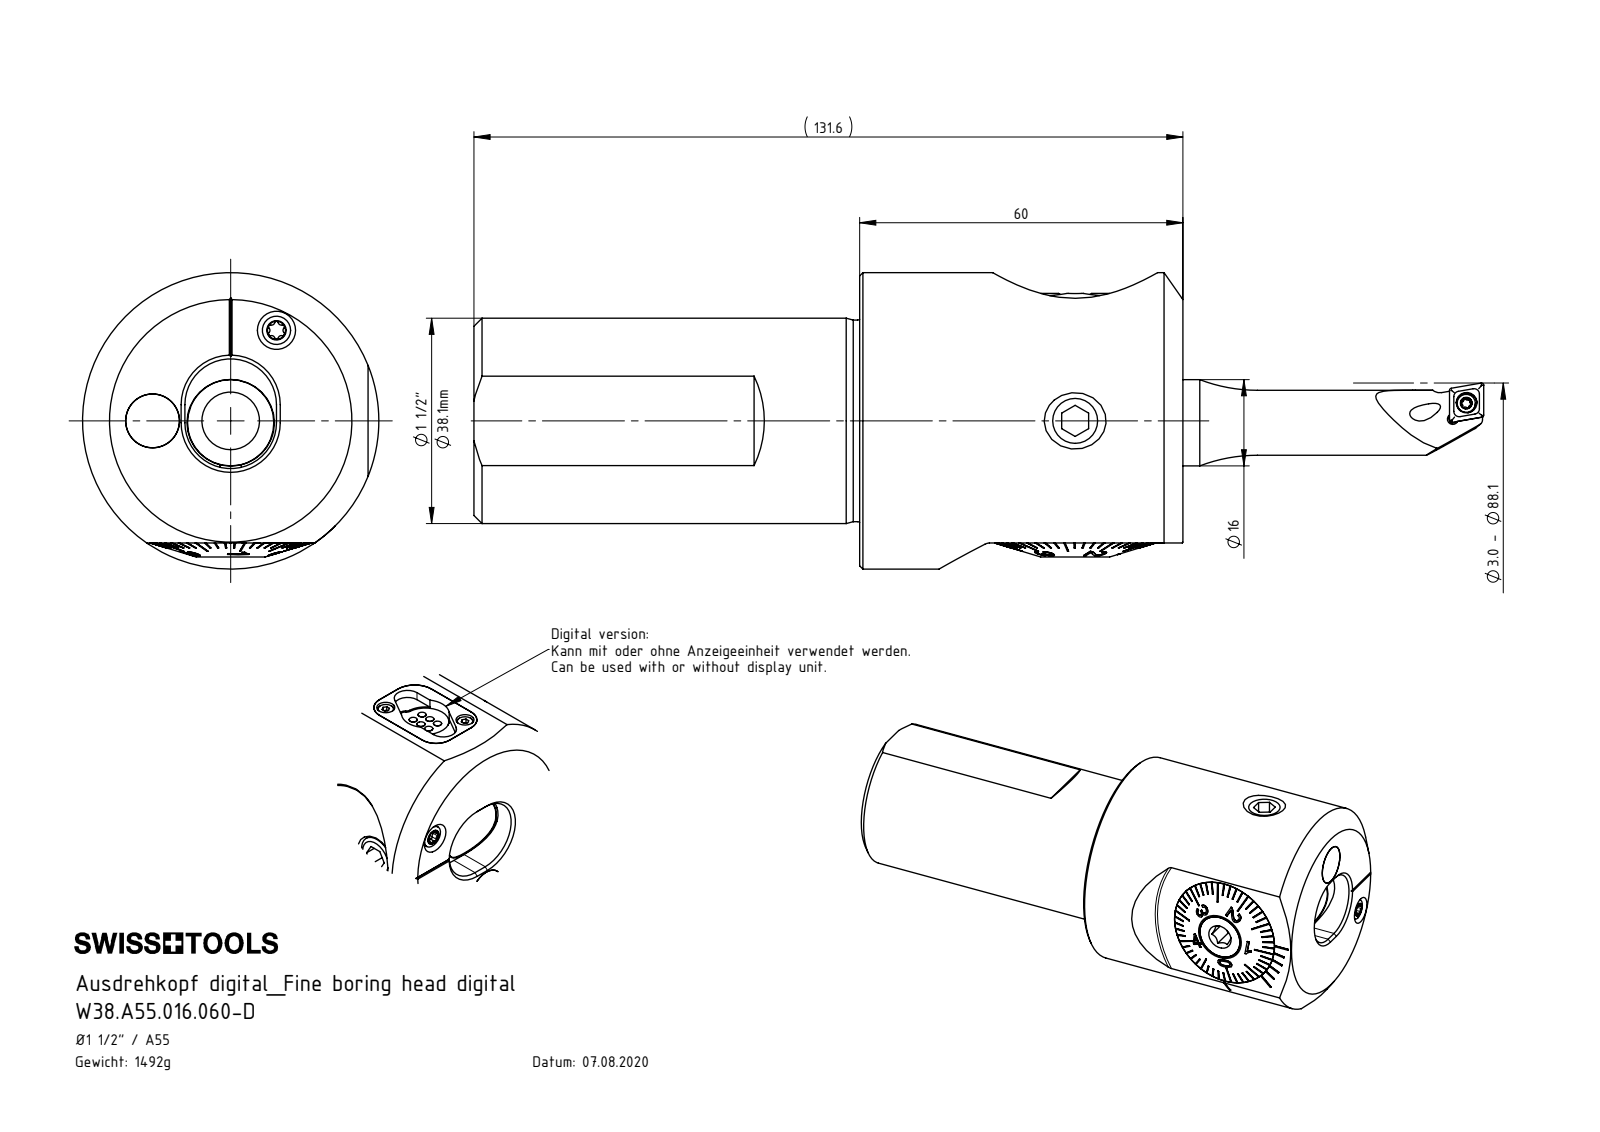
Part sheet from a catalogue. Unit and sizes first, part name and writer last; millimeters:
Units: millimetres
Overall size (bounding box): 131.6 × 55 × 55
Round holes (diameter × count): ⌀1.6 ×3, ⌀4.2 ×3, ⌀8.5 ×3, ⌀2.2 ×2, ⌀3.3 ×1, ⌀8 ×1, ⌀10 ×1, ⌀10.1 ×1, ⌀10.7 ×1, ⌀11.1 ×1, ⌀11.4 ×1, ⌀12.4 ×1
Round bosses / shafts (diameter × count): ⌀1.9 ×6, ⌀10 ×3, ⌀3.8 ×2, ⌀2 ×2, ⌀55 ×1, ⌀38.1 ×1, ⌀37.4 ×1, ⌀30 ×1
Partial cylindrical surfaces — rounded edges, fillets, slot ends (radius × count): R0.34 ×6, R0.59 ×6, R1.1 ×6, R1.2 ×6, R0.5 ×4, R0.8 ×4, R1.4 ×4, R1.9 ×4
Main face-to-face distances: 60, 71.6, 131.6, 5.3, 42.65, 2.8, 2.5, 6.5, 3.7, 1.2
Hole centre spacings: 14.5, 7.25, 9.52, 0.35, 18.83, 19.04, 19.14, 28.48
Volume: 190 793 mm³ · Surface area: 50 370 mm²
Bodies: 33 solids, 1009 faces (480 planar, 215 cylindrical, 314 other)
Part name (STEP PRODUCT): W38-A55.DA3.060_A_Fertigbearbeitung; Fxx-BG7.DA1.0xx_B_F55; DIN 3771 - 17x2; A55-BG1.DA4.041 (+8 more)
STEP written by: SolidWorks 2022 (CONFIG_CONTROL_DESIGN)
